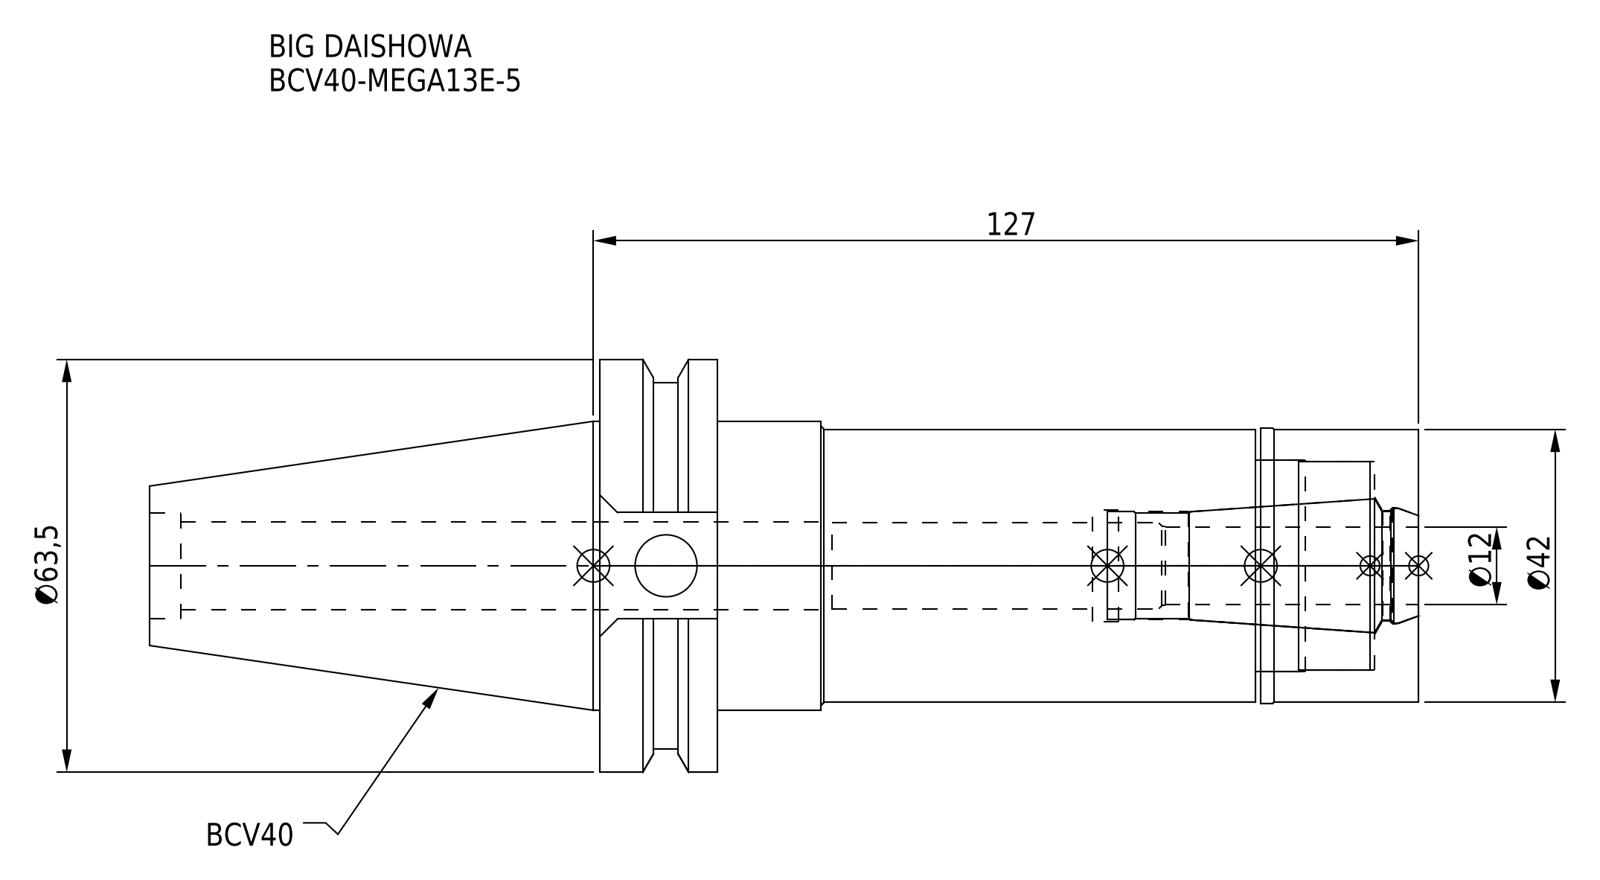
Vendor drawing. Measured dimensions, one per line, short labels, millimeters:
name: BCV40-MEGA13E-5; BCV40ME13050-012_ASM.stp; DXF_TEMP_ASSY_ASM_4_ASM.stp; BCV40-MEGA13E-5-120.stp (+3 more)
written by: SolidWorks 2019 (CONFIG_CONTROL_DESIGN)
unit: mm
bodies: 2 solids, 90 faces (30 planar, 42 cylindrical, 18 other)
size: 195.25 × 63.5 × 61.35
volume: 234 474 mm³; area: 45 723 mm²
holes: 1× ⌀9.53, 1× ⌀13.3, 1× ⌀13.6, 1× ⌀16.32, 1× ⌀16.6, 1× ⌀17, 1× ⌀17.2, 1× ⌀17.9, 1× ⌀32, 1× ⌀32.5
bosses: 1× ⌀63.5, 1× ⌀56.36, 1× ⌀44.45, 1× ⌀42.3, 1× ⌀42
face distances: 18.05, 107.95, 126, 25.1, 24.3, 83.65, 101.7, 0.8, 82.85, 100.9
